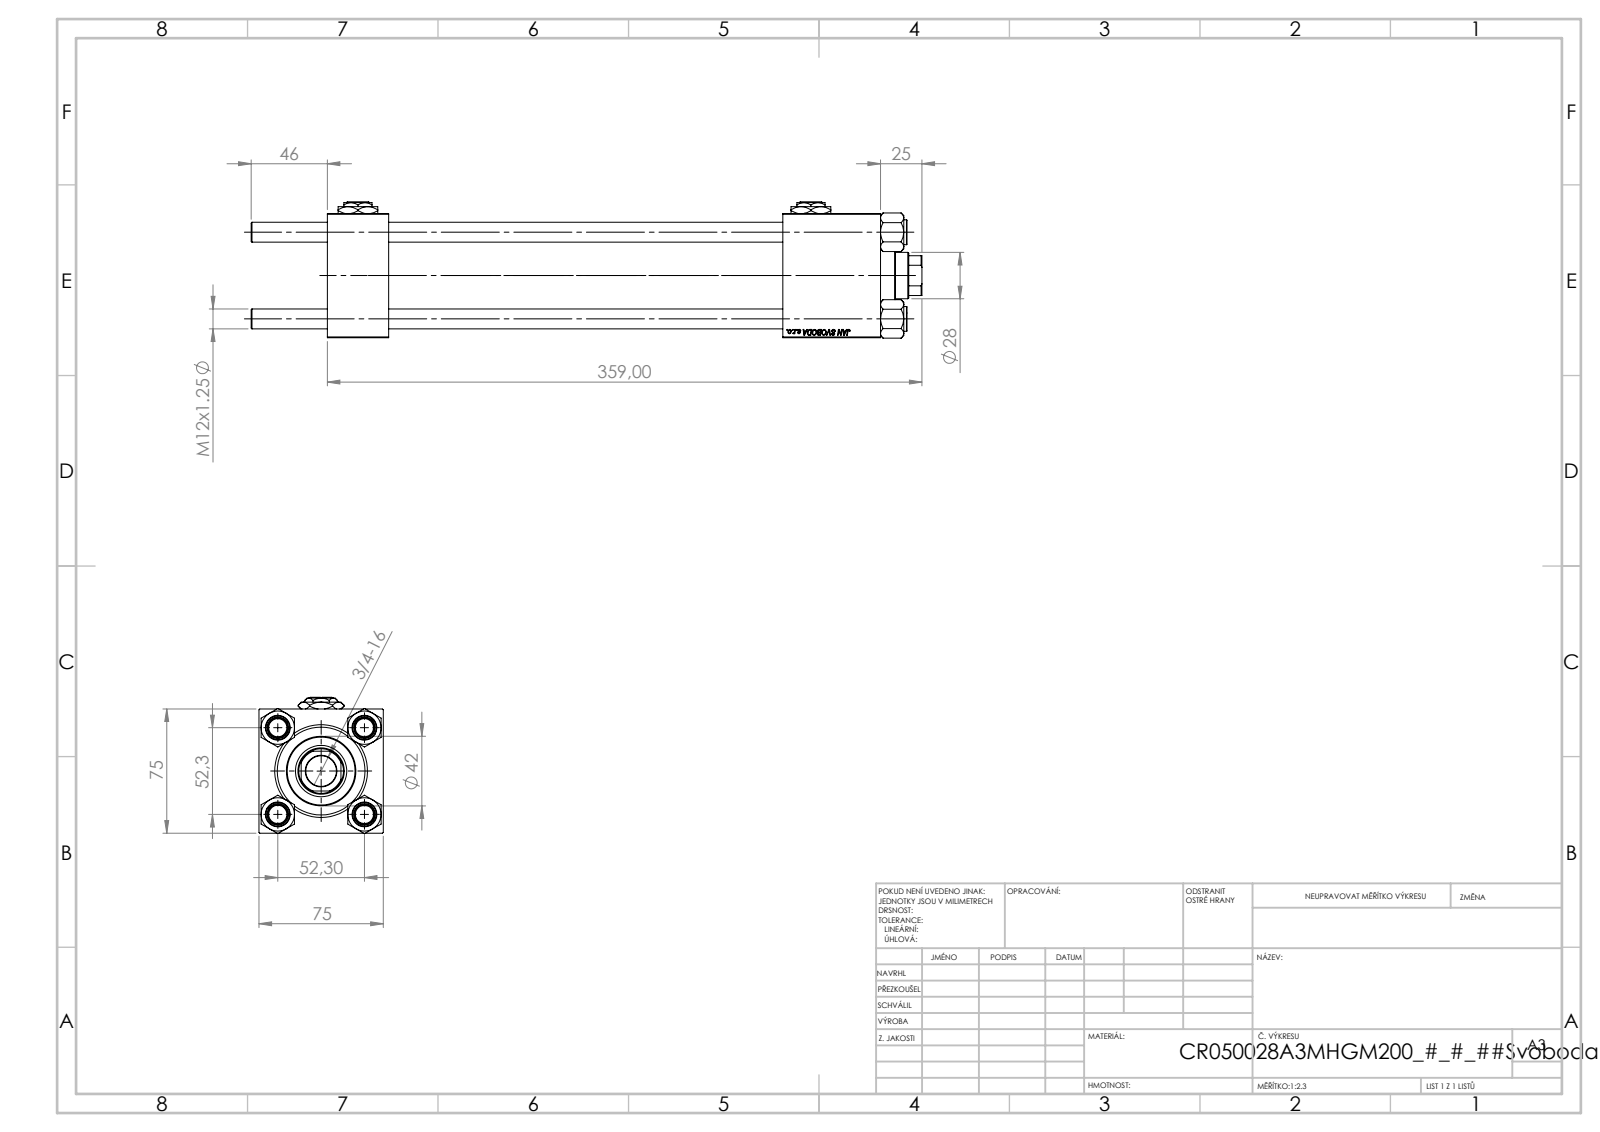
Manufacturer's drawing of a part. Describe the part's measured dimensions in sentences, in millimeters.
The part is named "CR025_012_A_0_G_A_G_M_020_+#_##_TYCINKA; V215CR_VCP; NUT_M5; Zatka_pro_OIL_PORT (+2 more)". Its 3-D file was written by "SolidWorks 2019 (CONFIG_CONTROL_DESIGN)". It is 13 solids with 1233 faces: 567 planar, 88 cylindrical and 578 other. Overall it measures 405 by 82.27 by 75 millimeters. Its volume is 979 263 cubic millimeters and its surface area 274 785 square millimeters. Round holes: 4 of diameter 12, 2 of diameter 7, 2 of diameter 20.96, 2 of diameter 30, 1 of diameter 18.5, 1 of diameter 28, 1 of diameter 31, 1 of diameter 41, 1 of diameter 50, 1 of diameter 53. Round bosses or shafts: 4 of diameter 15, 1 of diameter 56, 1 of diameter 42. Partial cylindrical surfaces (rounded edges, fillets, slot ends): 1 of radius 13.5. The main face-to-face distances are 75, 37, 334, 297, 275, 59, 238, 305.3, 268.3, 30.3. The hole center spacings are 36.98, 52.3, 73.96, 273.5.
